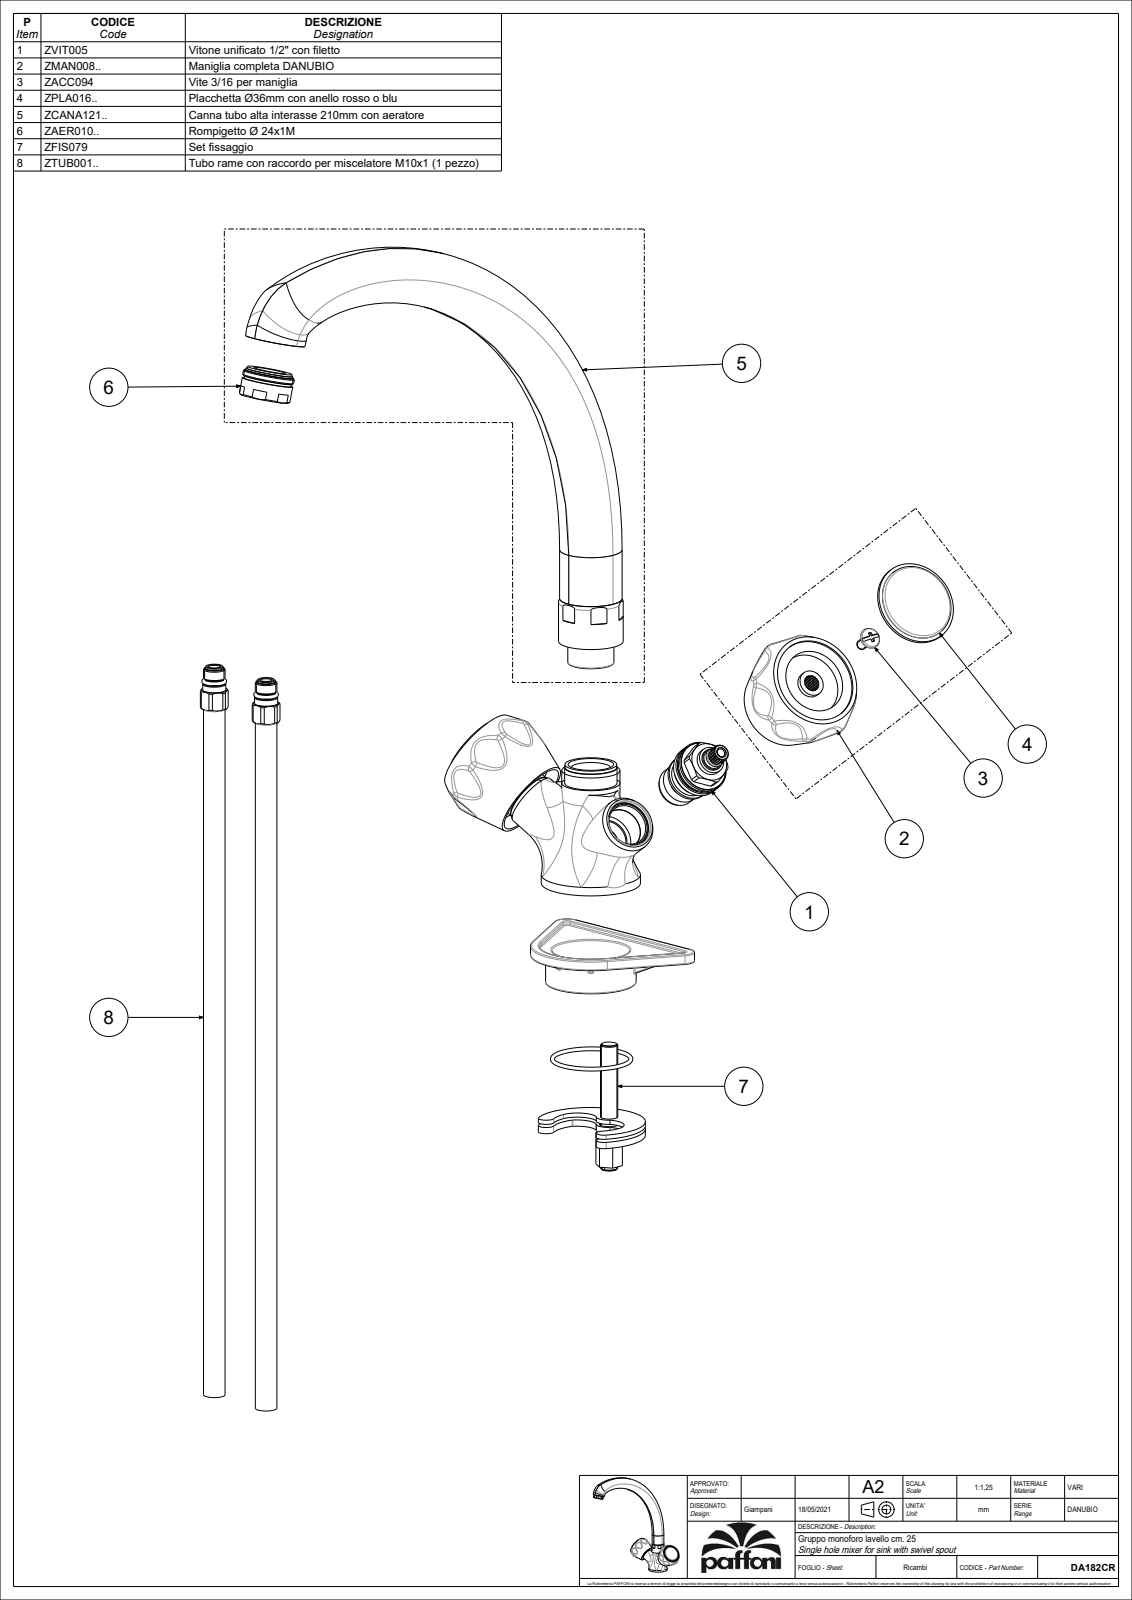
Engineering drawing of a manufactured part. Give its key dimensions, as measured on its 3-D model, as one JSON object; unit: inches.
{"part_name": "DA182CR", "step_written_by": "CREO PARAMETRIC BY PTC INC, 2020044 (CONFIG_CONTROL_DESIGN)", "units": "inches", "bodies": {"solids": 2, "faces": 363, "planar": 64, "cylindrical": 90, "other": 209}, "overall_size": [10.303, 9.587, 5.744], "volume_in3": 12.84, "surface_area_in2": 148.7, "round_holes": [[0.354, 4], [0.433, 2], [0.709, 2], [0.748, 2], [0.846, 2], [0.866, 2], [0.236, 1], [0.268, 1], [0.591, 1], [0.65, 1], [0.681, 1], [0.713, 1]], "round_bosses_or_shafts": [[1.516, 2], [1.024, 2], [1.811, 1], [1.339, 1], [1.181, 1], [0.945, 1], [0.937, 1], [0.866, 1]], "partial_cylinders_radius": [[0.839, 16], [0.728, 1]], "face_to_face_distances": [0.799, 1.39, 0.016, 1.406, 2.626, 2.902, 0.276, 1.819, 0.807, 1.083], "hole_center_spacings": [0.276, 0.547, 0.472, 0.551]}
